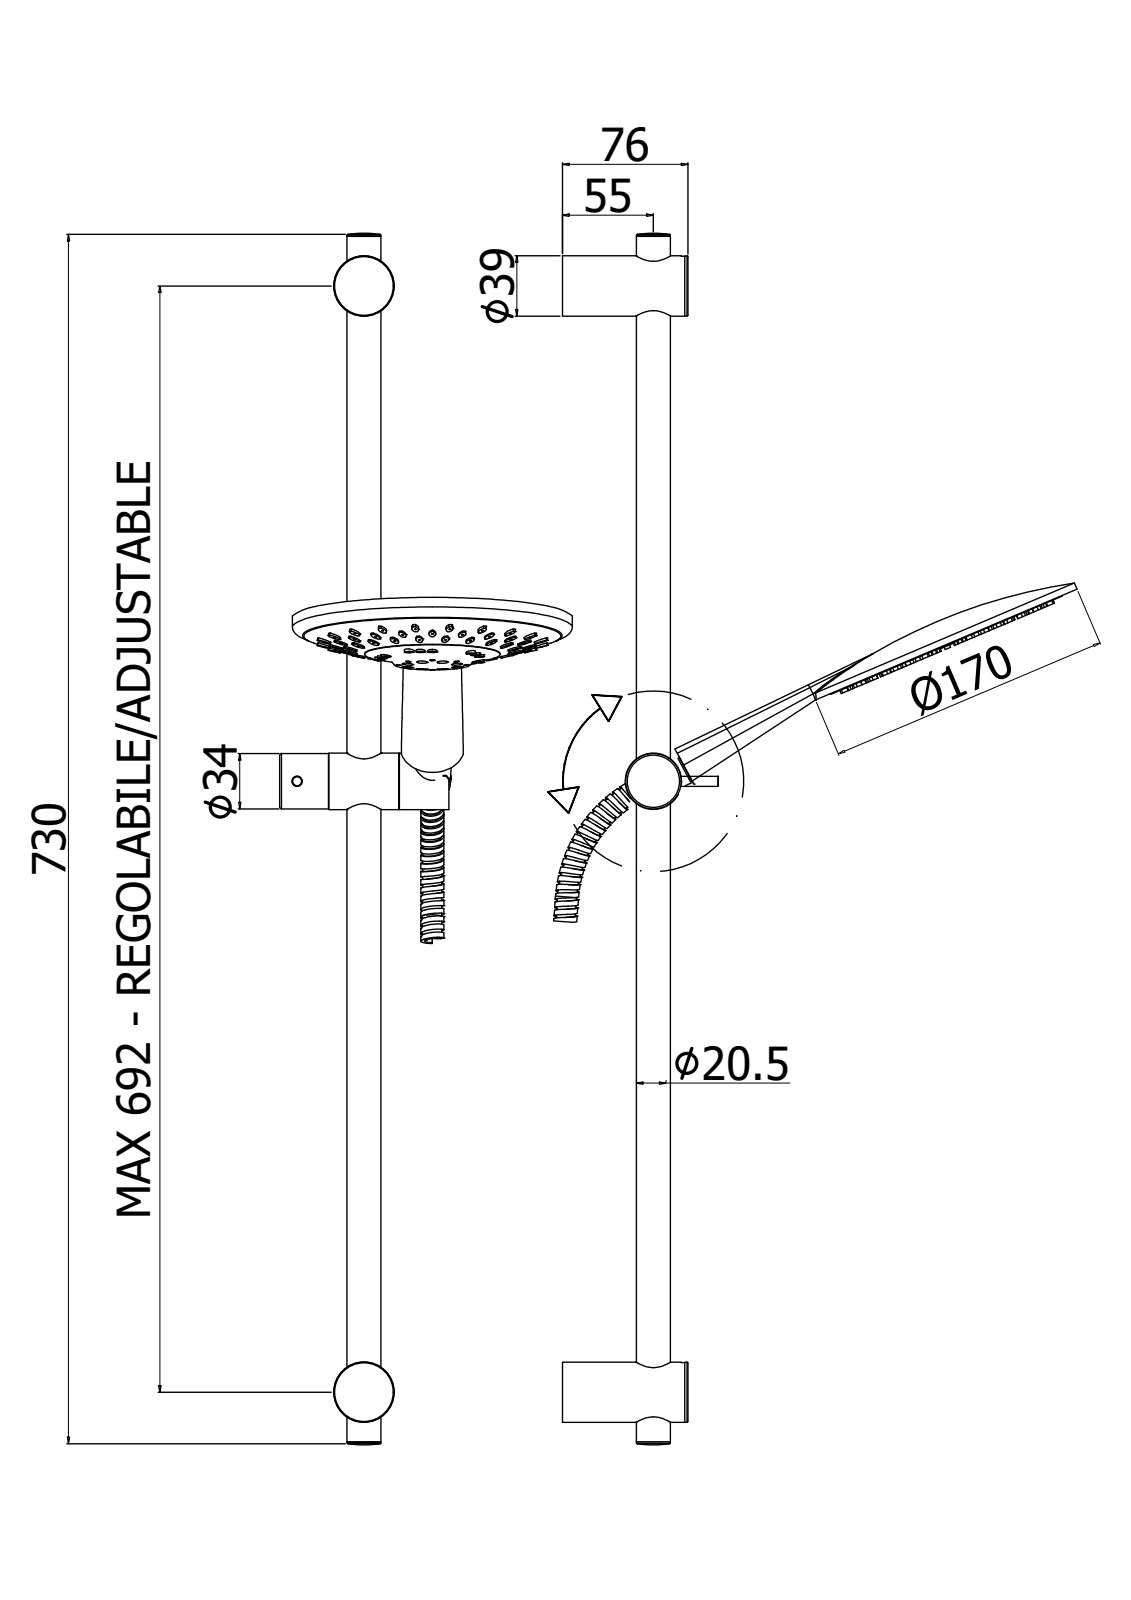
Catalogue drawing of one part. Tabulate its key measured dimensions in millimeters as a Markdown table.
| quantity | value |
| --- | --- |
| part name | M50520-020_3; M50330-013_1; M50520-011_1; M50520-012_1 (+8 more) |
| STEP written by | CREO PARAMETRIC BY PTC INC, 2020044 (CONFIG_CONTROL_DESIGN) |
| units | millimeters |
| bodies | 26 solids, 2083 faces (829 planar, 811 cylindrical, 443 other) |
| overall size | 734 × 179.1 × 107.39 |
| volume | 156 536 mm³ |
| surface area | 271 529 mm² |
| round holes (diameter × count) | 0.6 × 90, 3 × 2, 4 × 2, 5.4 × 2, 11.2 × 2, 15 × 2, 21 × 2, 22.5 × 2, 27 × 2, 31 × 2, 3.3 × 1, 3.6 × 1 |
| round bosses / shafts (diameter × count) | 31.2 × 3, 36.5 × 2, 35 × 2, 25 × 2, 22.4 × 2, 20.5 × 2, 19.8 × 2, 12 × 2 |
| partial cylindrical surfaces (radius × count) | 1.75 × 180, 1.5 × 9, 0.6 × 8, 0.3 × 6, 0.5 × 6, 0.2 × 4, 1.6 × 2, 2.4 × 2 |
| main face-to-face distances | 1.1, 366.51, 367.61, 365.41, 74, 1, 0.5, 3, 36, 33 |
| hole center spacings | 34.39, 12, 16.35, 34.73, 30, 42, 43.42, 18.54 |
